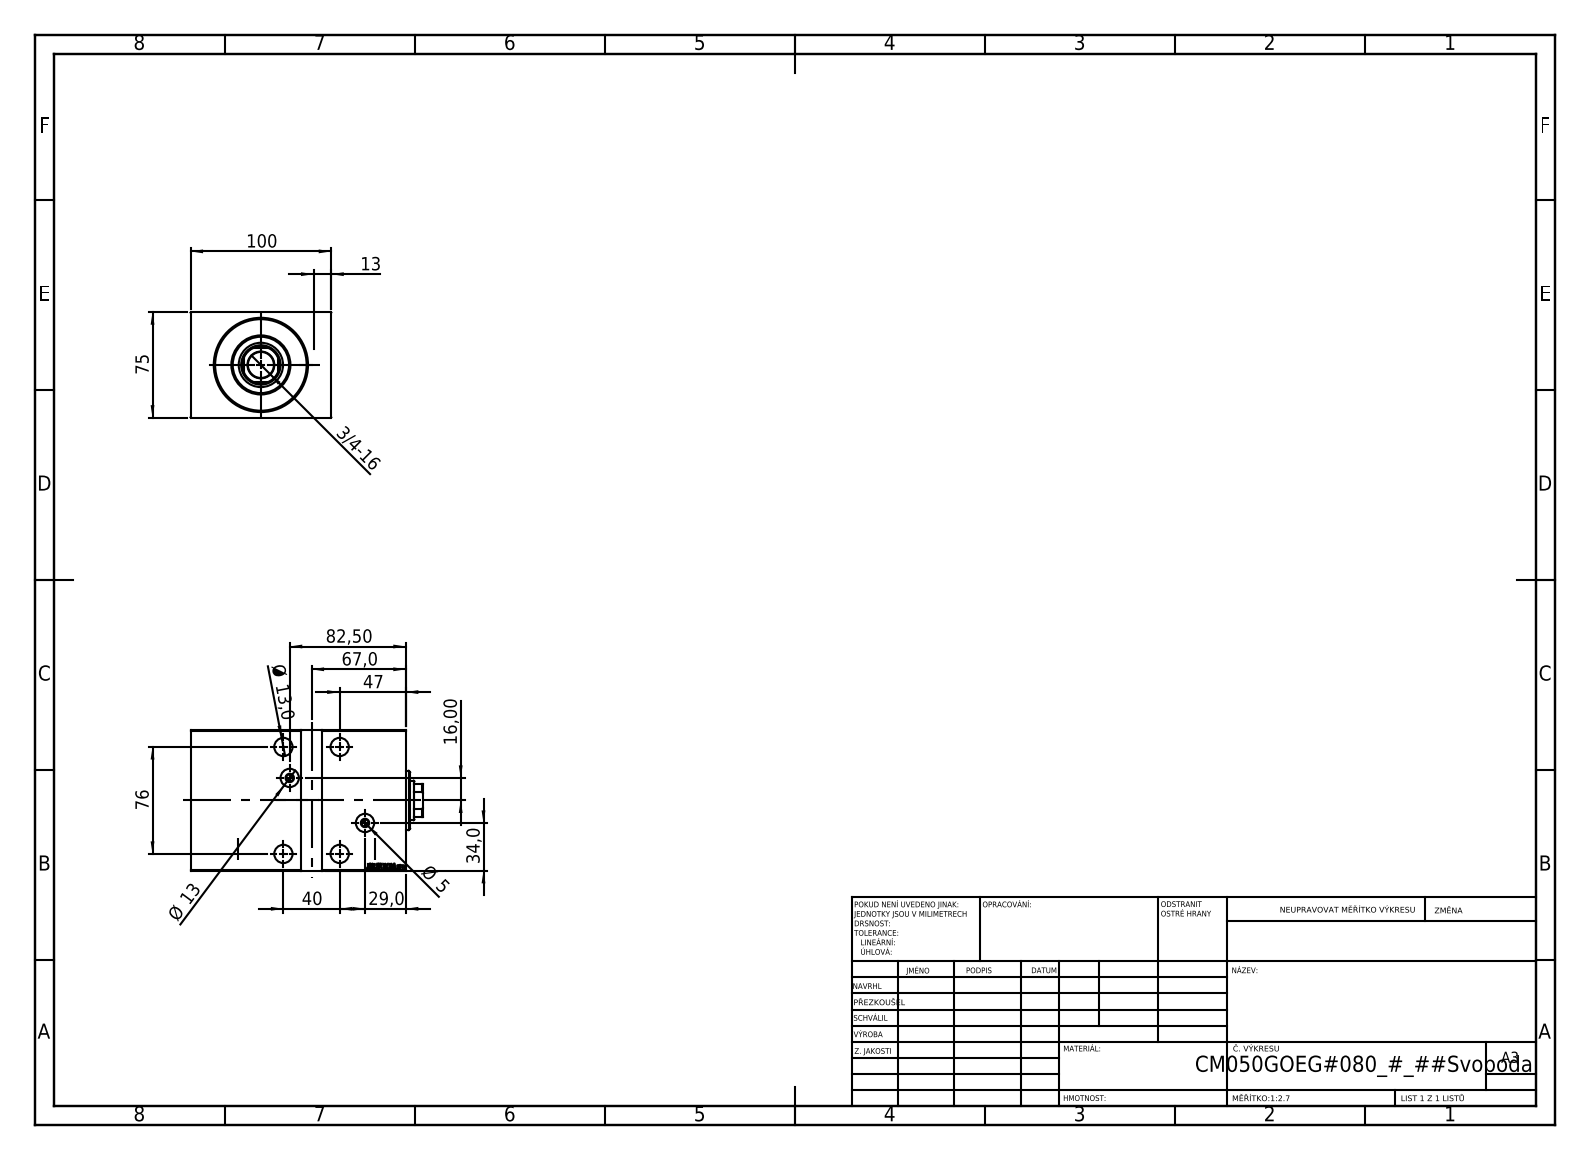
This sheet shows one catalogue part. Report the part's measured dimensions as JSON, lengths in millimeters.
{"part_name": "Zatka_OIL_PORT; V450CM_G_VCP; V450CM_VC_G; V450CM_G_Body", "step_written_by": "SolidWorks 2019 (CONFIG_CONTROL_DESIGN)", "units": "millimeters", "bodies": {"solids": 5, "faces": 896, "planar": 442, "cylindrical": 56, "other": 398}, "overall_size": [165, 100, 75], "volume_mm3": 972239, "surface_area_mm2": 135435, "round_holes": [[13, 6], [19, 4], [5, 2], [18.5, 1], [28, 1], [31.5, 1], [50, 1], [52, 1], [65, 1]], "round_bosses_or_shafts": [[18, 2], [6, 2], [42, 1]], "partial_cylinders_radius": [[13.5, 1]], "face_to_face_distances": [75, 100, 153, 5, 14, 139, 134, 148, 70, 61], "hole_center_spacings": [40, 76, 85.88, 22.46, 28.43, 41.76, 54.19, 56.92]}
